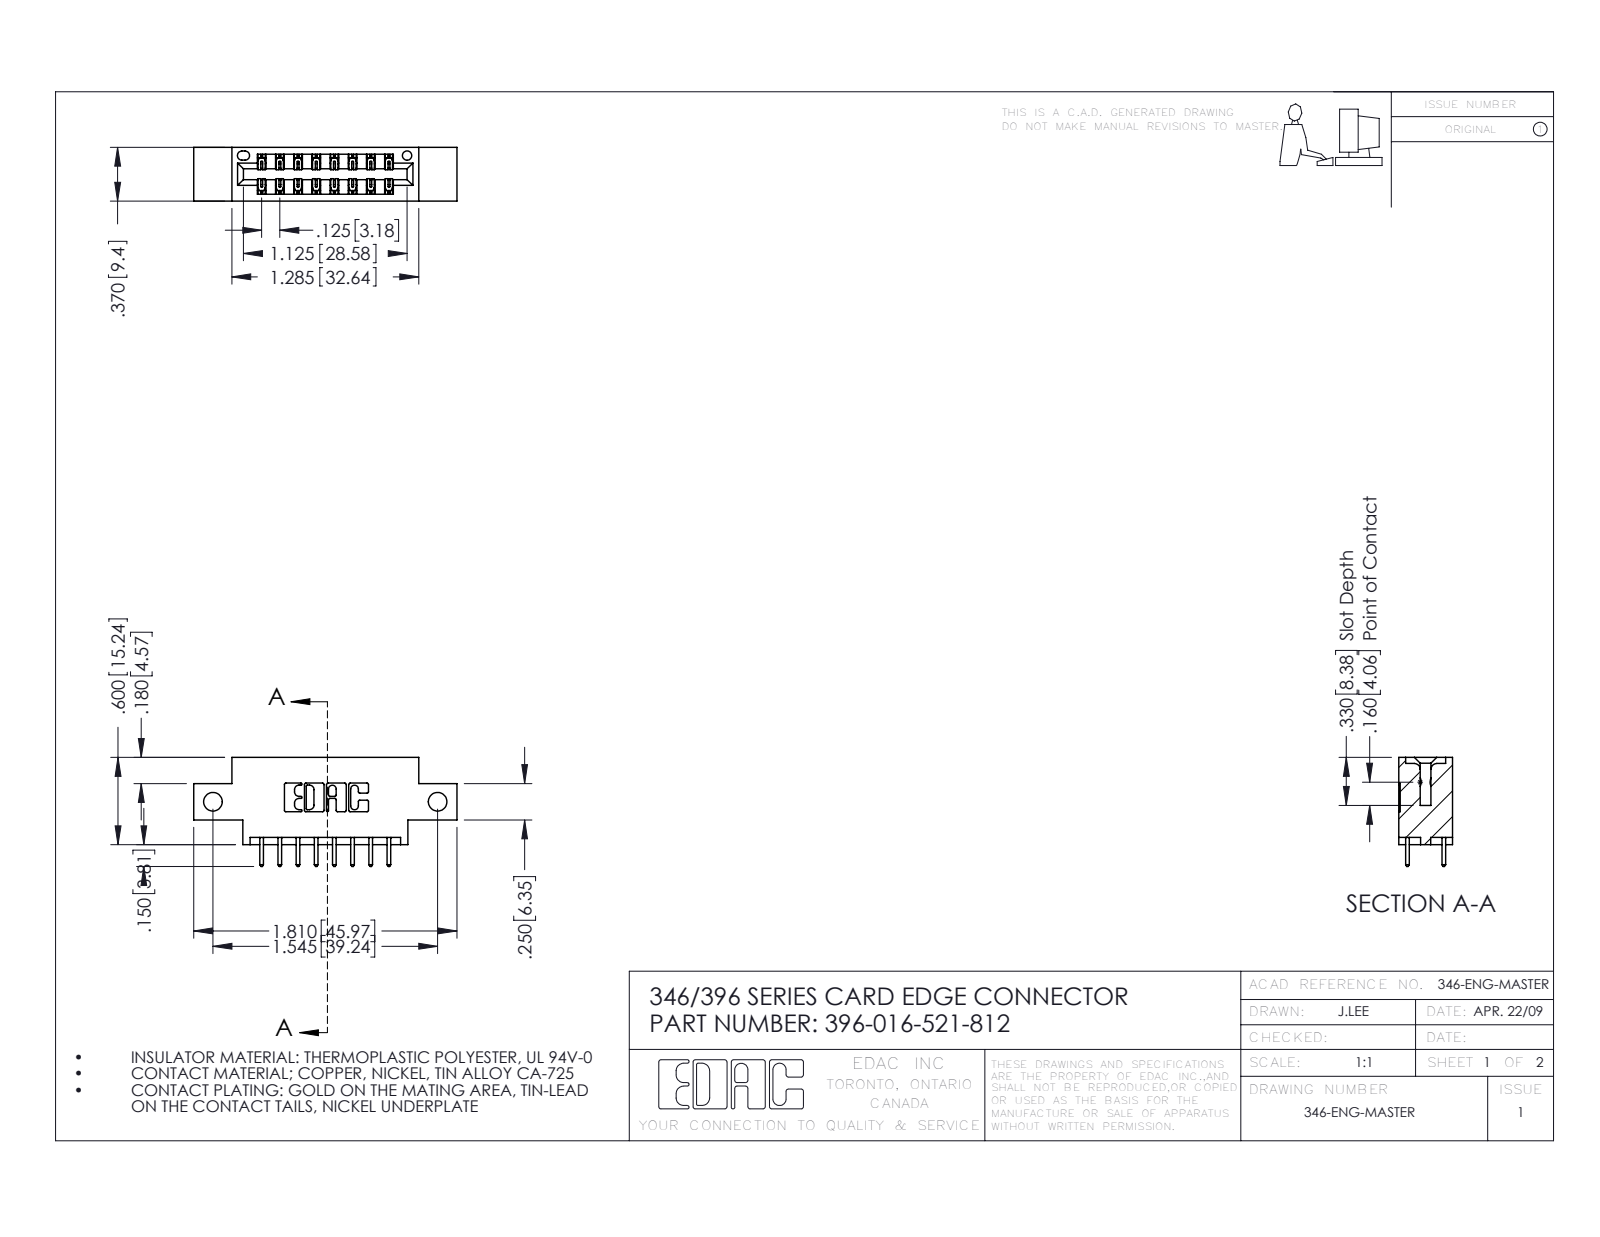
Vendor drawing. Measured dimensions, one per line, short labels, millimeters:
name: 346 Part_0.170 Offset - Side Mount; 396-016-521-812; 345-292-001_345-293-121
written by: SolidWorks 2016 (CONFIG_CONTROL_DESIGN)
unit: mm
bodies: 17 solids, 958 faces (640 planar, 318 cylindrical, 0 other)
size: 46 × 19.1 × 9.4
volume: 3 970 mm³; area: 4 921 mm²
holes: 2× ⌀3.3, 1× ⌀1.6
rounds: 24× R0.2, 22× R0.3, 16× R0.3, 6× R0.2, 6× R0.8, 3× R0.7, 2× R0.4, 2× R0.6
face distances: 6.4, 9.4, 1.2, 8.2, 1.8, 7.6, 0.6, 7, 3.8, 5.6
hole spacings: 39.2
